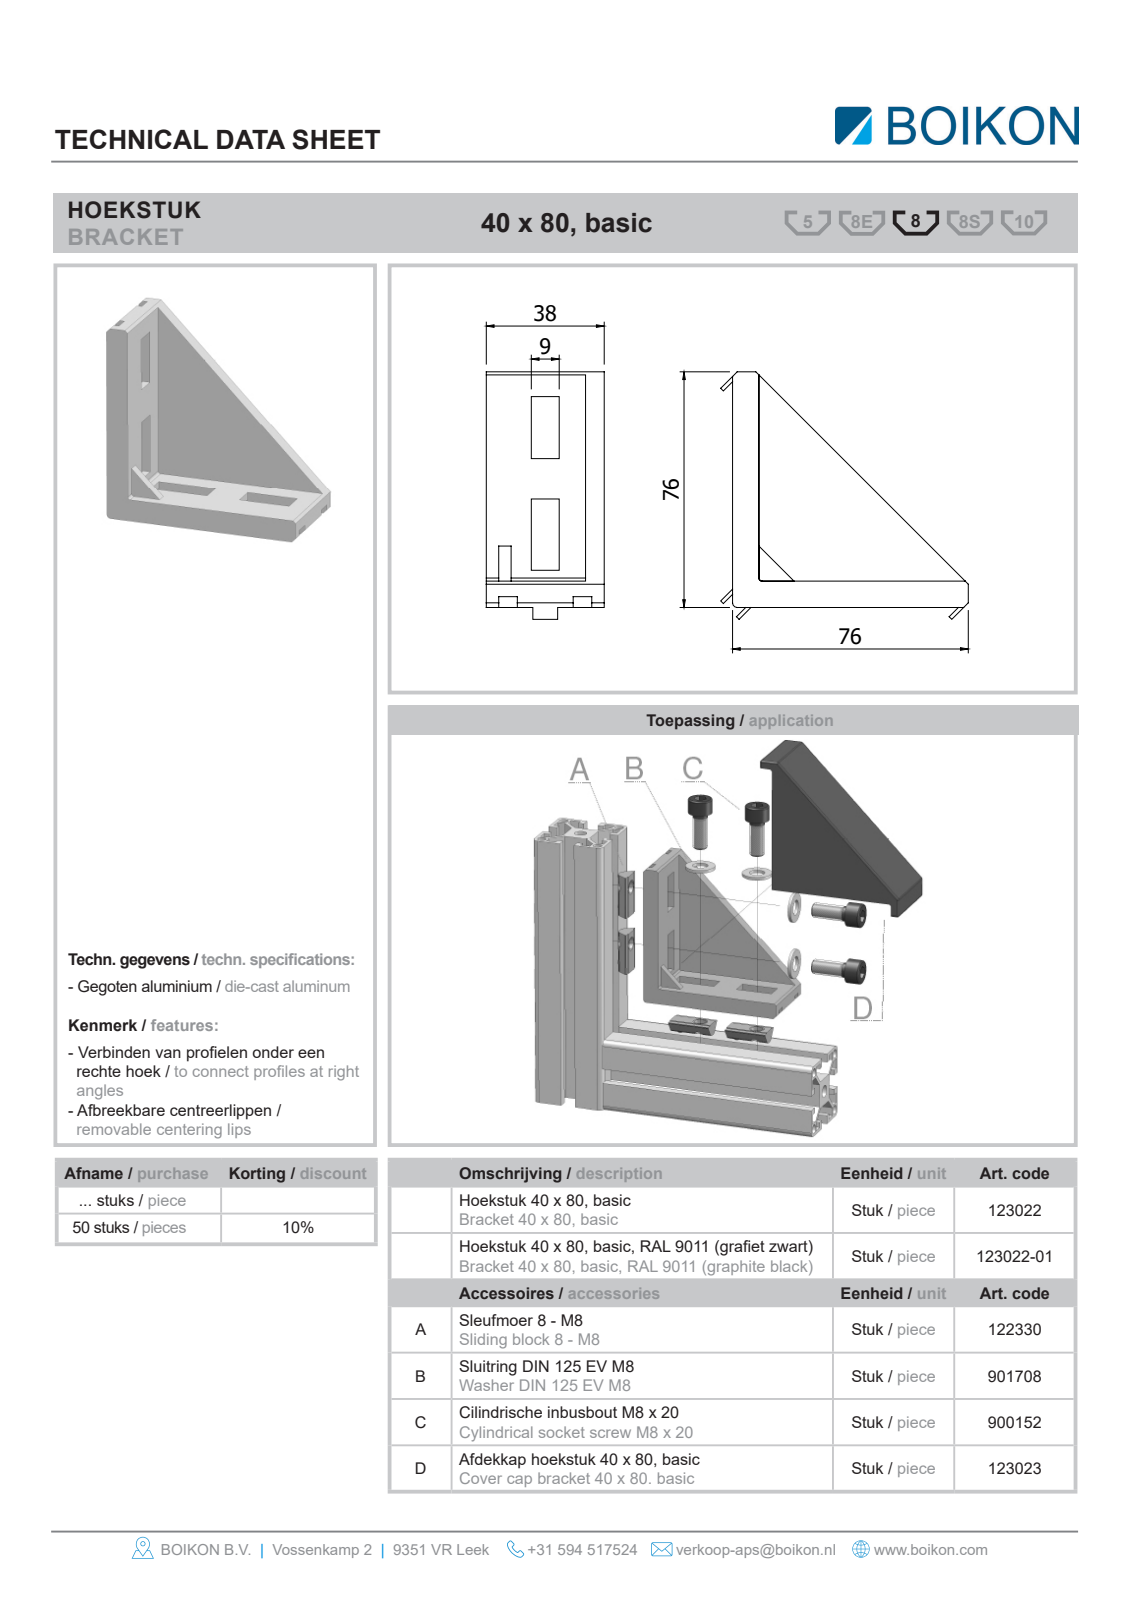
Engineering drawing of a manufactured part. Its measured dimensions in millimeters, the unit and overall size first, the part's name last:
Units: millimetres
Overall size (bounding box): 92.14 × 92.14 × 38
Round holes (diameter × count): ⌀8 ×4, ⌀8.4 ×4
Round bosses / shafts (diameter × count): ⌀16 ×4, ⌀13 ×4, ⌀6.47 ×4
Partial cylindrical surfaces — rounded edges, fillets, slot ends (radius × count): R1 ×15, R0.5 ×4, R2 ×4, R5 ×2, R1.5 ×1
Main face-to-face distances: 38, 5.99, 8.5, 4, 6, 35, 3, 29, 32, 4.5
Hole centre spacings: 32.5
Volume: 88 392 mm³ · Surface area: 45 589 mm²
Bodies: 14 solids, 347 faces (247 planar, 76 cylindrical, 24 other)
Part name (STEP PRODUCT): Root; 123022HOEKSTUK 40X80 BASICBOIKON; 123023AFDEKKAP HOEKSTUK 40X80 BASICBOIKON; 122330Sleufmoer 8 - M8 met kogelBOIKON (+2 more)
STEP written by: HiCAD 2013 1802.4 Build 509 (AUTOMOTIVE_DESIGN)
